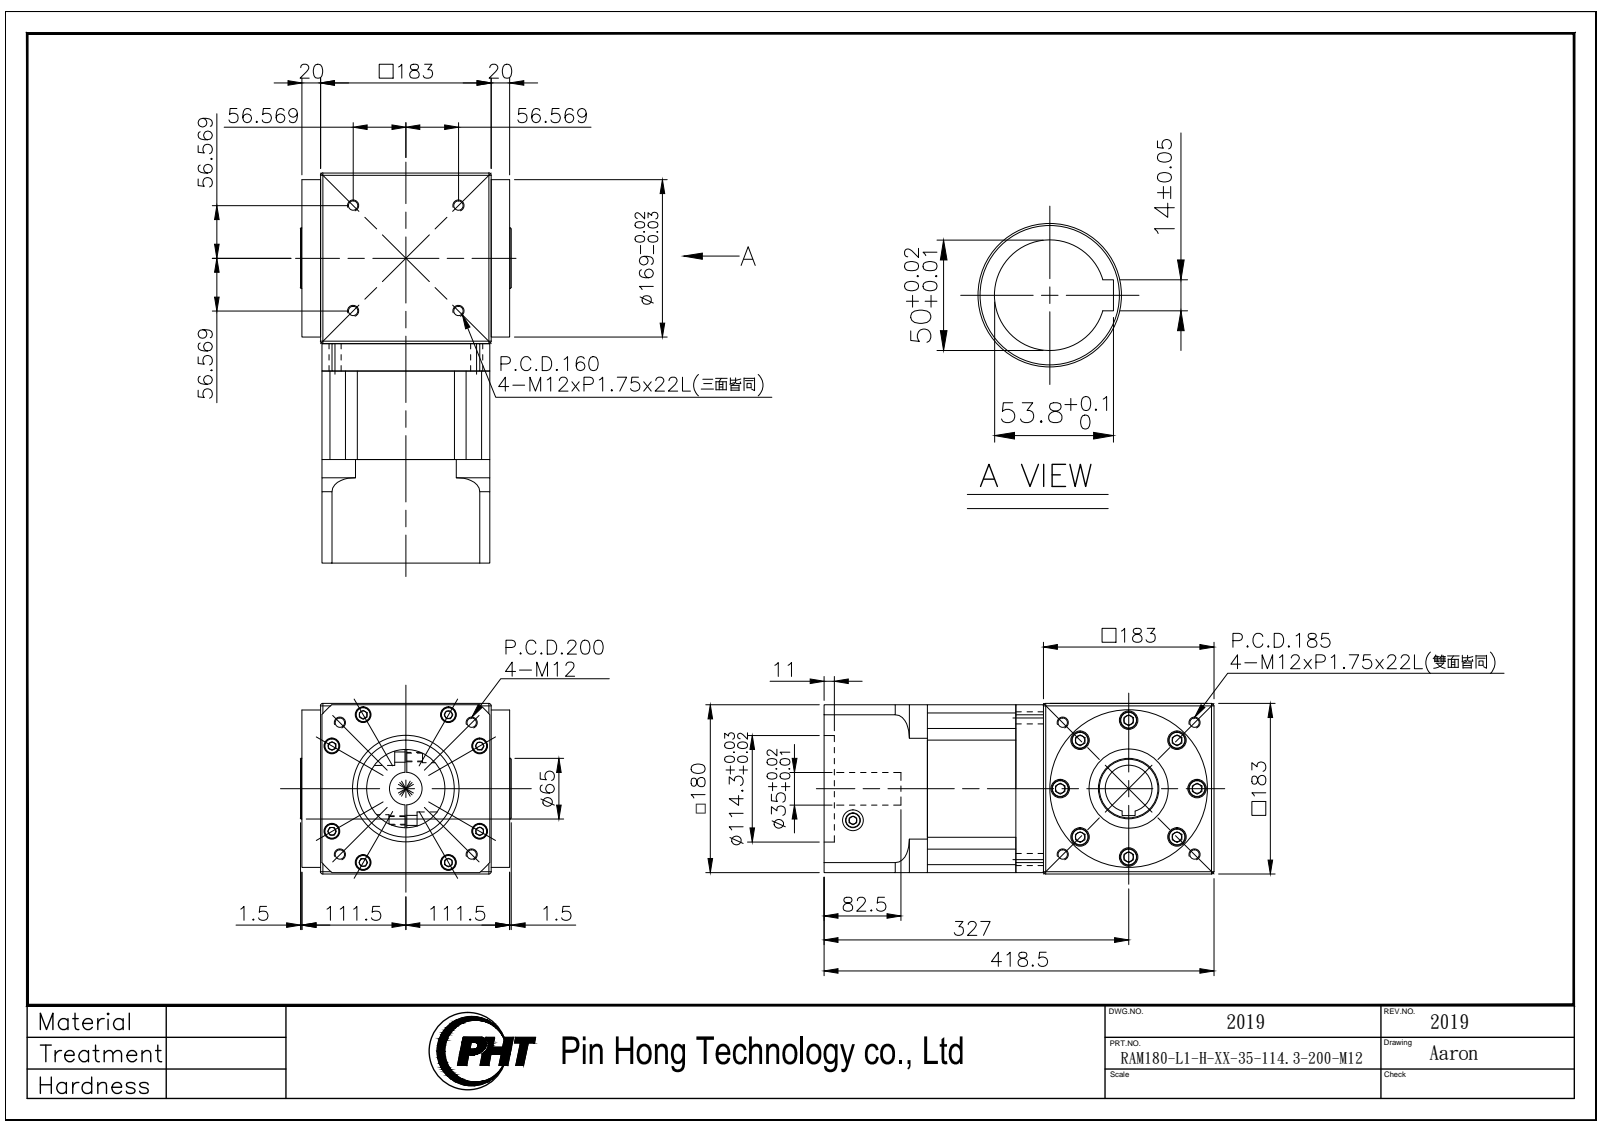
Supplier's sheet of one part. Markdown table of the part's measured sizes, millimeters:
| quantity | value |
| --- | --- |
| part name | RAM180-L1-XX-H-35-114.3-200-M12_2019 |
| STEP written by | SolidWorks 2016 (AUTOMOTIVE_DESIGN) |
| units | millimeters |
| bodies | 4 solids, 788 faces (348 planar, 276 cylindrical, 164 other) |
| overall size | 418.5 × 226 × 183 |
| volume | 13 300 000 mm³ |
| surface area | 797 042 mm² |
| round holes (diameter × count) | 10.2 × 20, 11 × 8, 14 × 8, 17 × 8, 20 × 8, 13 × 4, 22.5 × 2, 35 × 1, 50 × 1, 51 × 1, 104 × 1, 114.3 × 1 |
| round bosses / shafts (diameter × count) | 18.3 × 8, 16 × 8, 18 × 4, 169 × 1, 160 × 1, 85 × 1, 84 × 1, 65 × 1 |
| partial cylindrical surfaces (radius × count) | 12.5 × 4, 104 × 1, 105 × 1, 120 × 1 |
| main face-to-face distances | 1.5, 181.5, 183, 180, 95, 124.5, 29.5, 212.5, 307.5, 21.5 |
| hole center spacings | 91.5, 25.12, 26.38, 30.43, 56.25, 65.91, 73.5, 103.94 |
